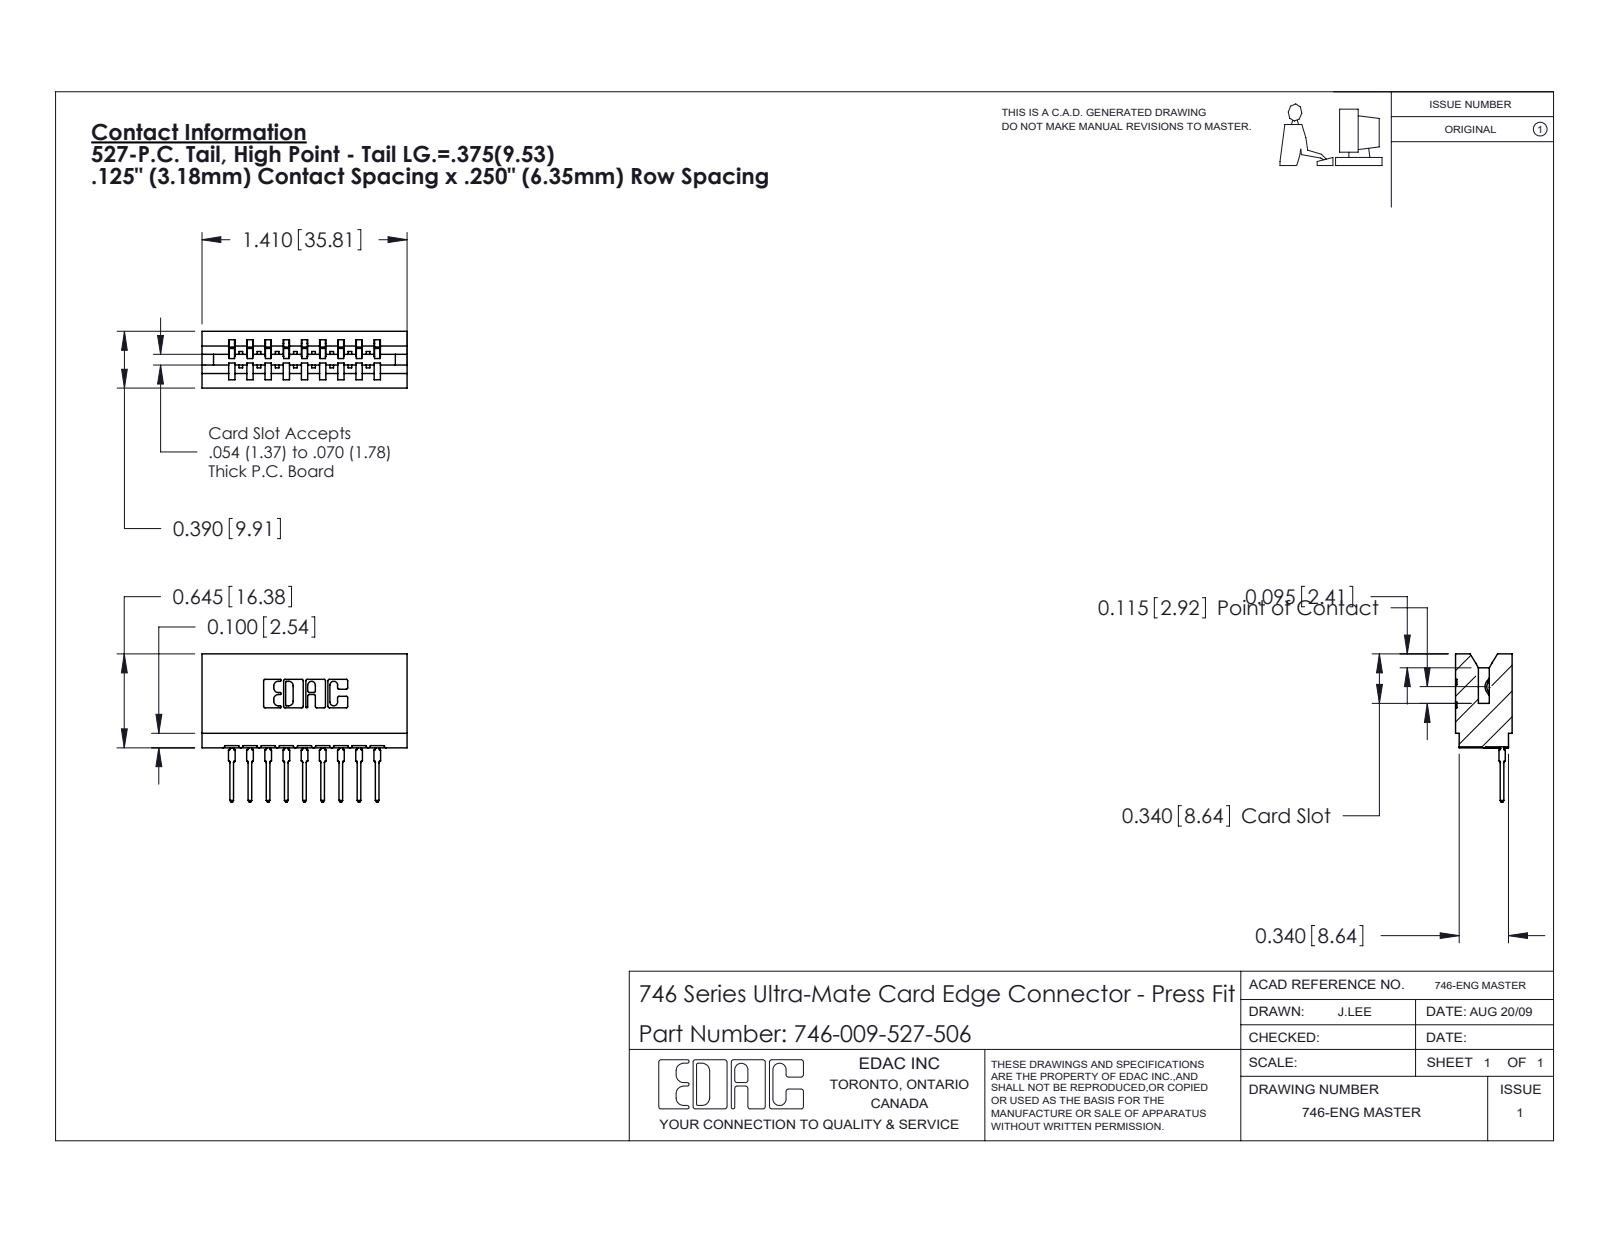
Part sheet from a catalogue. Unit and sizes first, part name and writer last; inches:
Units: inches
Overall size (bounding box): 1.41 × 1.019 × 0.39
Partial cylindrical surfaces — rounded edges, fillets, slot ends (radius × count): R0.01 ×22, R0.021 ×18, R0.015 ×10, R0.007 ×6, R0.031 ×6, R0.005 ×4, R0.011 ×4, R0.026 ×3
Main face-to-face distances: 0.25, 0.5, 0.042, 0.333, 0.125, 0.125, 0.292, 0.208, 0.057, 0.375
Volume: 0.257 in³ · Surface area: 8.114 in²
Bodies: 10 solids, 1070 faces (623 planar, 213 cylindrical, 234 other)
Part name (STEP PRODUCT): 746-292-001_527; 746 Part_.340 Slot Depth - 06; 746-009-527-506
STEP written by: SolidWorks 2020 (CONFIG_CONTROL_DESIGN)
